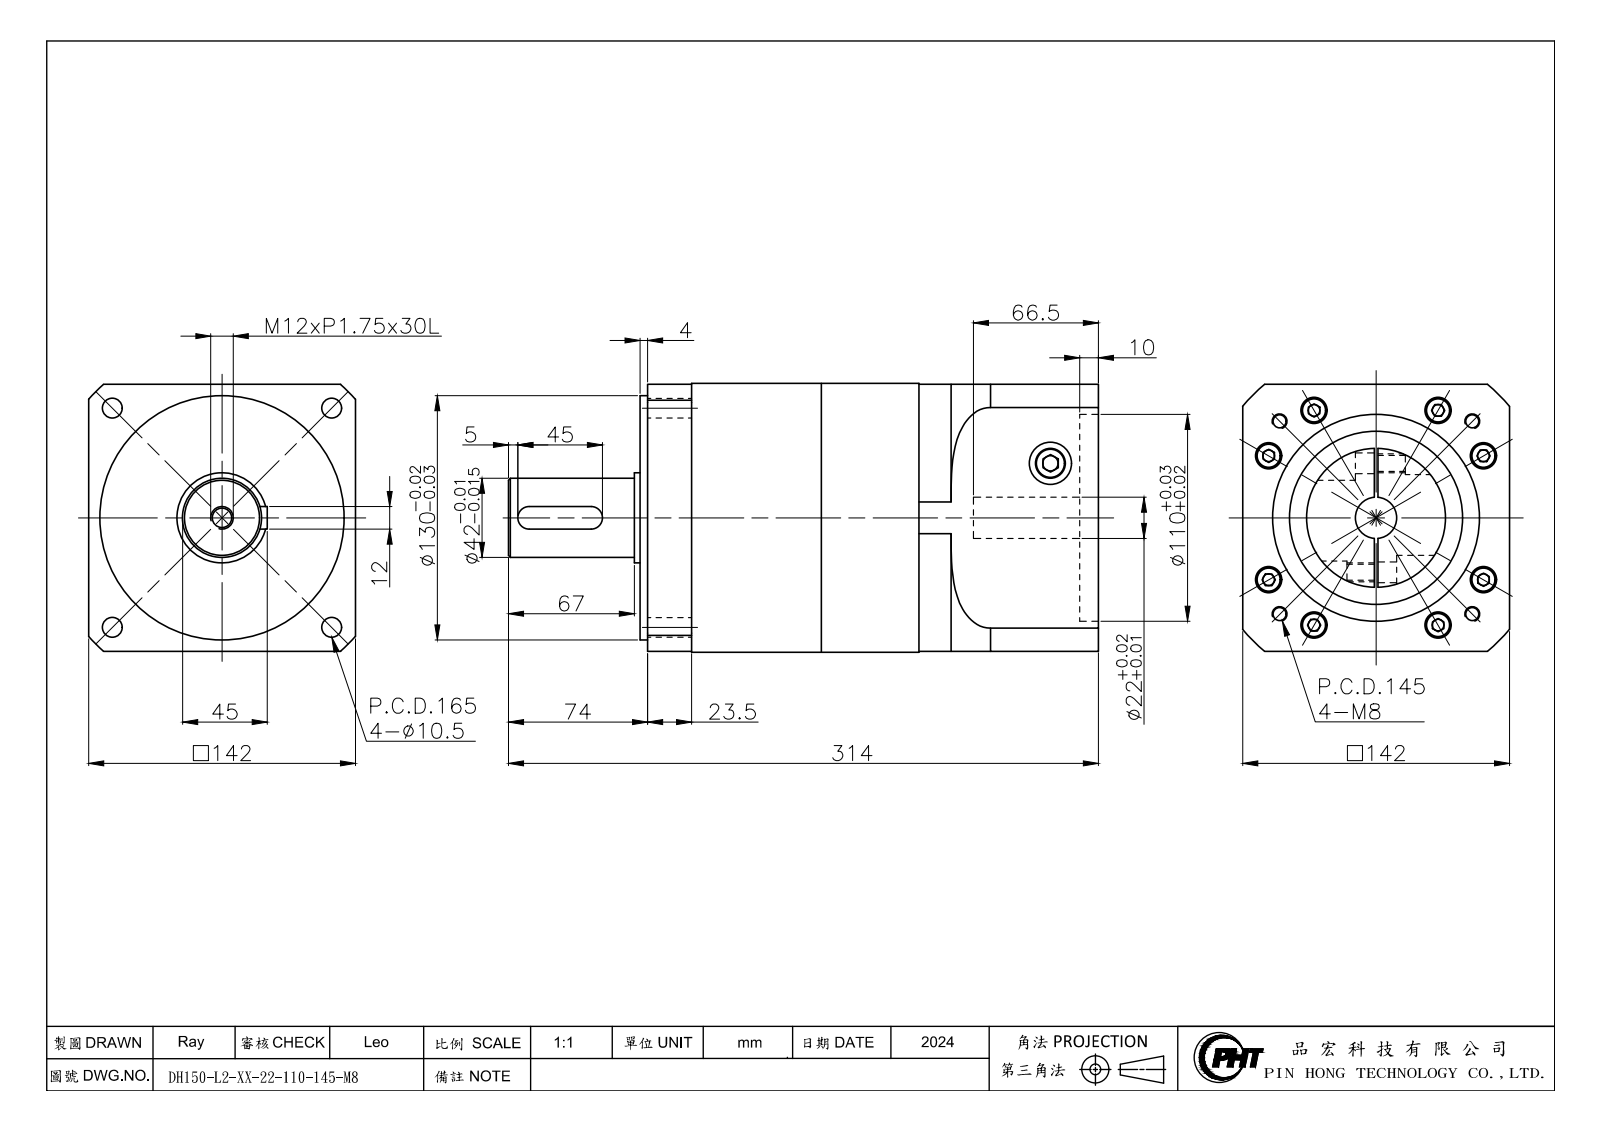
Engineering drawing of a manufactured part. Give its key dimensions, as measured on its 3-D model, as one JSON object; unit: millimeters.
{"part_name": "DH150-L2-XX-22-110-145-M8_2024", "step_written_by": "SolidWorks 2016 (CONFIG_CONTROL_DESIGN)", "units": "millimeters", "bodies": {"solids": 5, "faces": 268, "planar": 125, "cylindrical": 111, "other": 32}, "overall_size": [314, 143, 143], "volume_mm3": 4020000, "surface_area_mm2": 323402, "round_holes": [[9, 8], [14, 8], [6.8, 4], [10.5, 4], [22.5, 2], [10.2, 1], [22, 1], [42, 1], [92, 1], [110, 1]], "round_bosses_or_shafts": [[13, 8], [143, 1], [130, 1], [74, 1], [48, 1]], "partial_cylinders_radius": [[6, 2], [72, 1], [92.5, 1], [95, 1]], "face_to_face_distances": [69, 142, 96.5, 27.5, 147.5, 216.5, 244, 70, 4, 240], "hole_center_spacings": [66, 19.2, 25.37, 84.48, 91.35, 93.34, 109.84, 109.96]}
